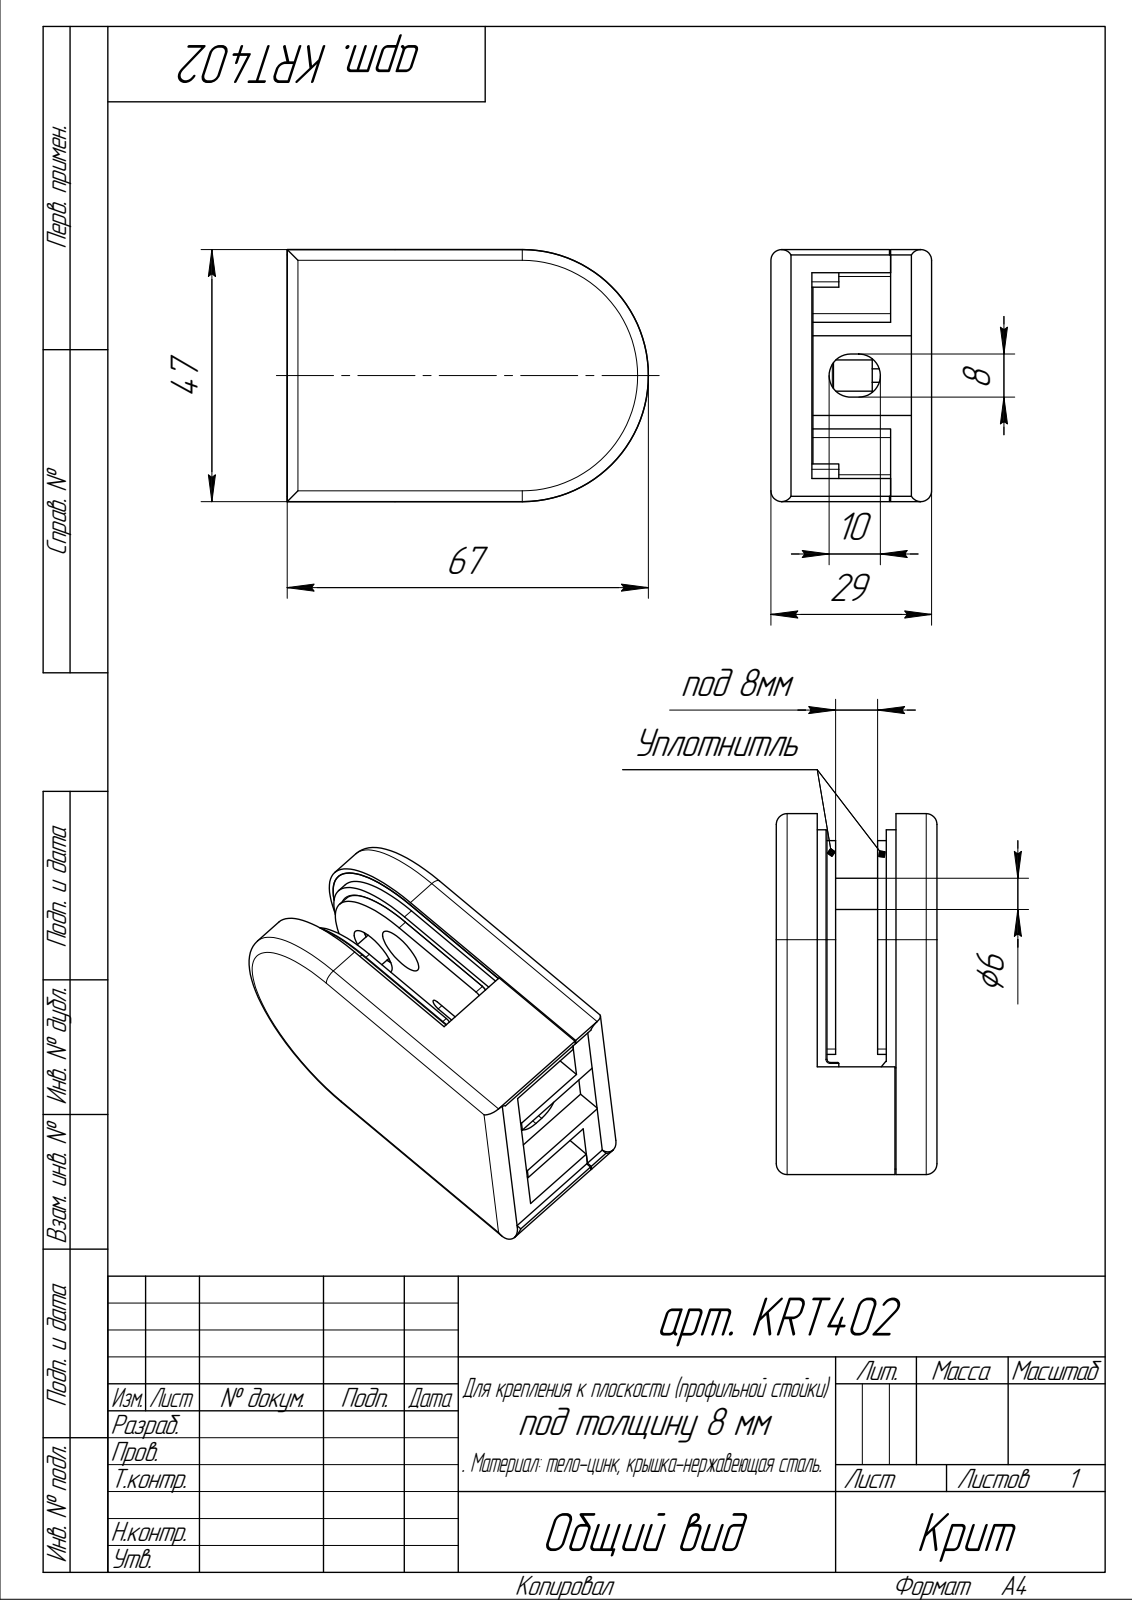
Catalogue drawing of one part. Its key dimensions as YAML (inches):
part_name: "Для крепления к плоскости (профильной стойки) под толщину 8 мм . Материал: тело-цинк, крышка-нержавеющая сталь.; Деталь"
step_written_by: "ASCON Math Kernel (AUTOMOTIVE_DESIGN)"
units: inches
bodies: {solids: 7, faces: 265, planar: 142, cylindrical: 102, other: 21}
overall_size: [2.638, 1.843, 1.173]
volume: 3.346
surface_area: 67.35
round_holes:
  - {diameter: 0.197, count: 2}
  - {diameter: 0.276, count: 2}
  - {diameter: 0.374, count: 2}
  - {diameter: 0.472, count: 2}
  - {diameter: 0.236, count: 1}
  - {diameter: 0.394, count: 1}
round_bosses_or_shafts:
  - {diameter: 0.228, count: 1}
partial_cylinders:
  - {radius: 0.008, count: 16}
  - {radius: 0.039, count: 12}
  - {radius: 0.079, count: 10}
  - {radius: 0.063, count: 8}
  - {radius: 0.016, count: 4}
  - {radius: 0.157, count: 2}
  - {radius: 0.024, count: 1}
  - {radius: 0.049, count: 1}
face_to_face_distances: [0.039, 0.26, 0.835, 0.874, 0.299, 1.134, 1.094, 0.433, 1.173, 0.575]
hole_center_spacings: [0.02, 0.491, 0.941, 1.205, 1.224, 1.469, 1.483, 1.591]
